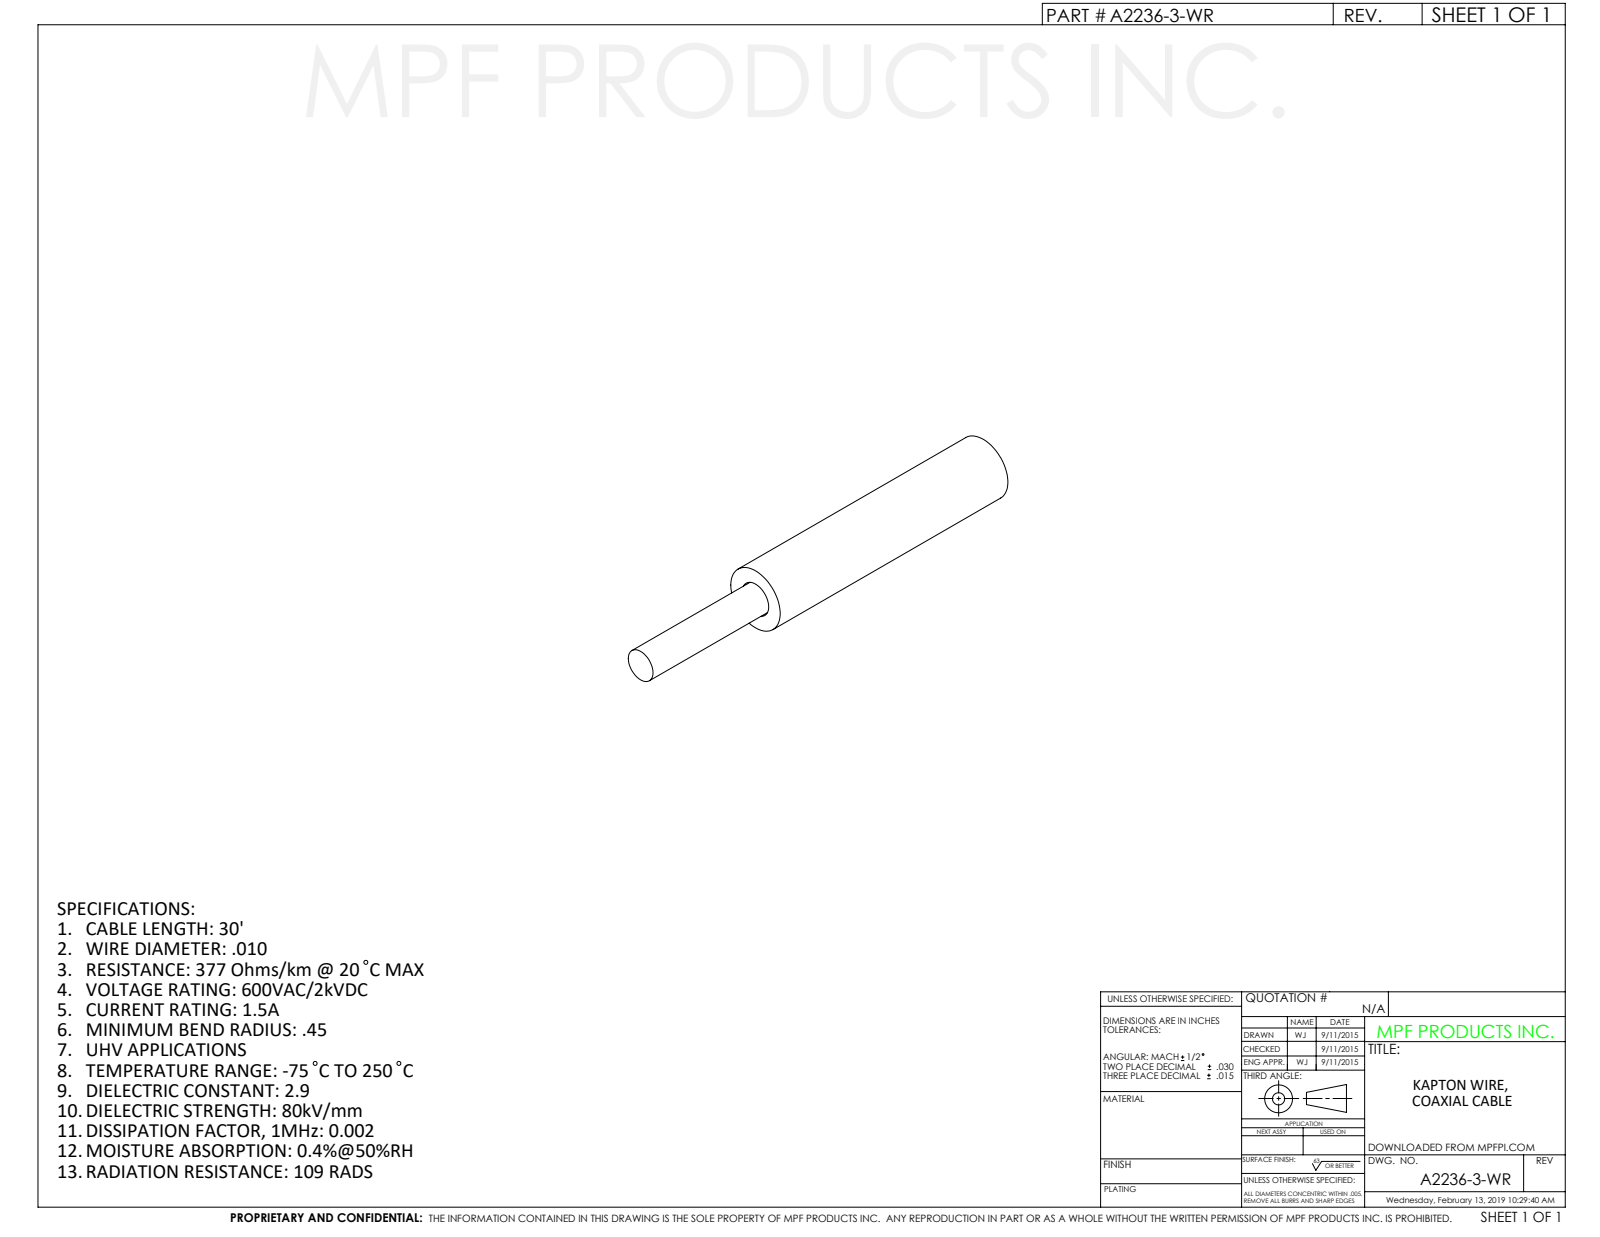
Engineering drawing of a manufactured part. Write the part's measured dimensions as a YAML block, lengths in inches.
part_name: "A2236-3-WR"
step_written_by: "SolidWorks 2012 (CONFIG_CONTROL_DESIGN)"
units: inches
bodies: {solids: 3, faces: 204, planar: 7, cylindrical: 55, other: 142}
overall_size: [0.203, 0.042, 0.042]
round_holes:
  - {diameter: 0.011, count: 1}
  - {diameter: 0.02, count: 1}
round_bosses_or_shafts:
  - {diameter: 0.042, count: 1}
  - {diameter: 0.04, count: 1}
  - {diameter: 0.02, count: 1}
  - {diameter: 0.01, count: 1}
face_to_face_distances: [0.1, 0.134, 0.034, 0.099, 0.035]
